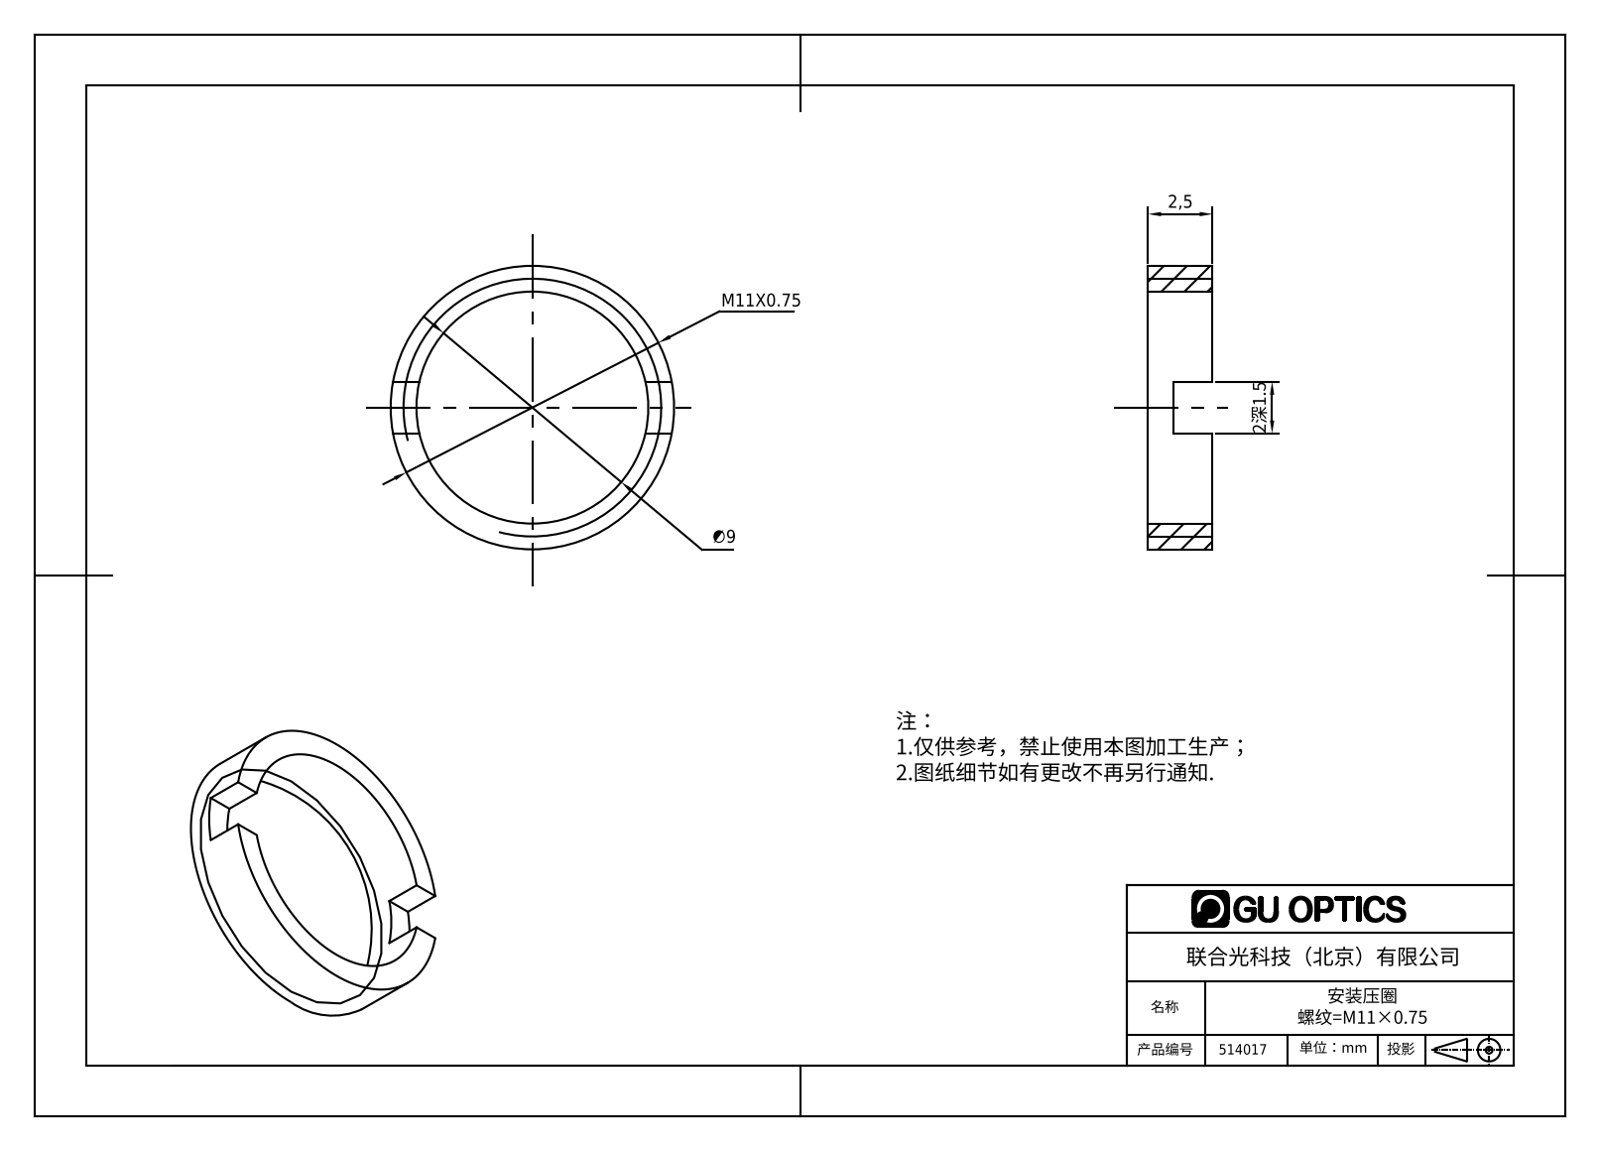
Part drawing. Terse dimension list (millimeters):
name: 514017
written by: SolidWorks 2016 (CONFIG_CONTROL_DESIGN)
unit: mm
bodies: 1 solid, 13 faces (9 planar, 4 cylindrical, 0 other)
size: 11 × 11 × 2.5
volume: 72 mm³; area: 214 mm²
holes: 1× ⌀9
bosses: 1× ⌀11
face distances: 2.5, 1, 1.5, 2
